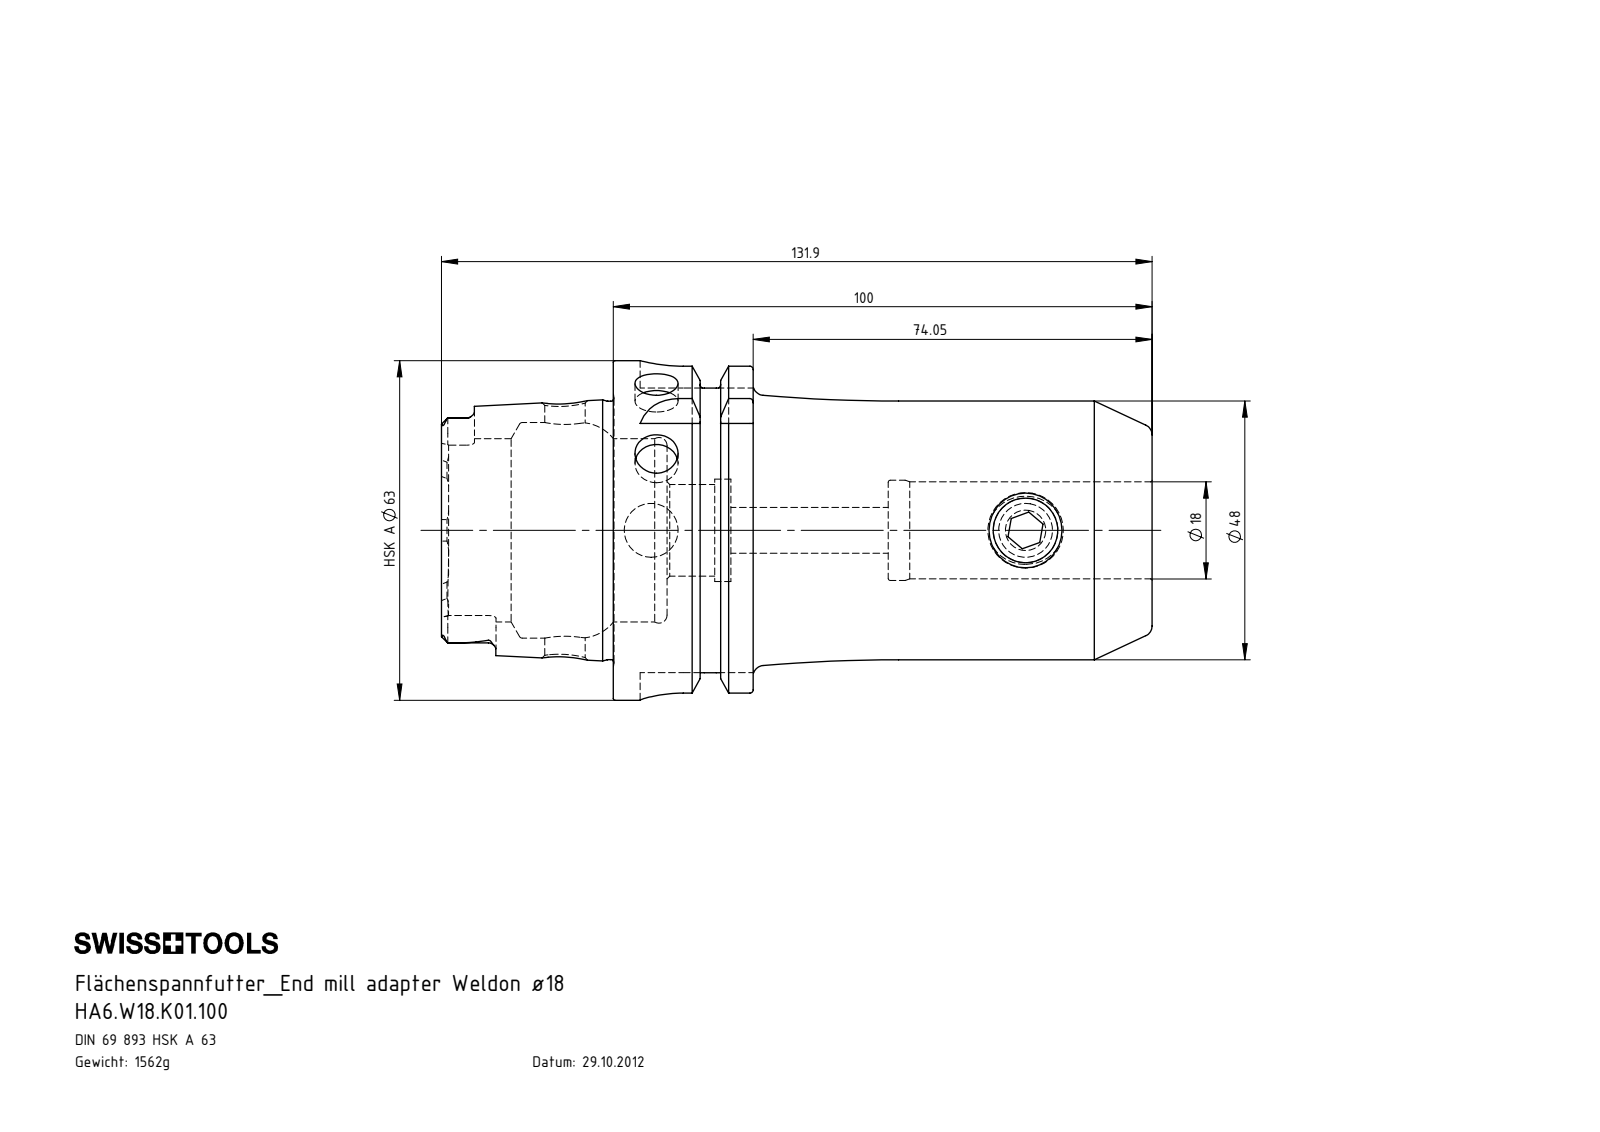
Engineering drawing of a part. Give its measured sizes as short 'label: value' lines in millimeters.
name: W16-ER1.001.016; HA6-W18.K01.100_A_Fertigbearbeitung; HA6-W18.K01.100
written by: SolidWorks 2012 (CONFIG_CONTROL_DESIGN)
unit: mm
bodies: 2 solids, 211 faces (59 planar, 57 cylindrical, 95 other)
size: 131.9 × 63 × 63
volume: 198 982 mm³; area: 37 574 mm²
holes: 2× ⌀8, 1× ⌀7.5, 1× ⌀8.5, 1× ⌀10, 1× ⌀12, 1× ⌀17, 1× ⌀18, 1× ⌀18.6, 1× ⌀19, 1× ⌀34, 1× ⌀40
bosses: 1× ⌀63, 1× ⌀54.95, 1× ⌀48, 1× ⌀47.94, 1× ⌀14
rounds: 6× R1.4, 4× R2.88, 4× R8
face distances: 100, 25.95, 74.05, 16, 9.95, 90.05, 31.9, 41.85, 57.85, 131.9
hole spacings: 69.5
